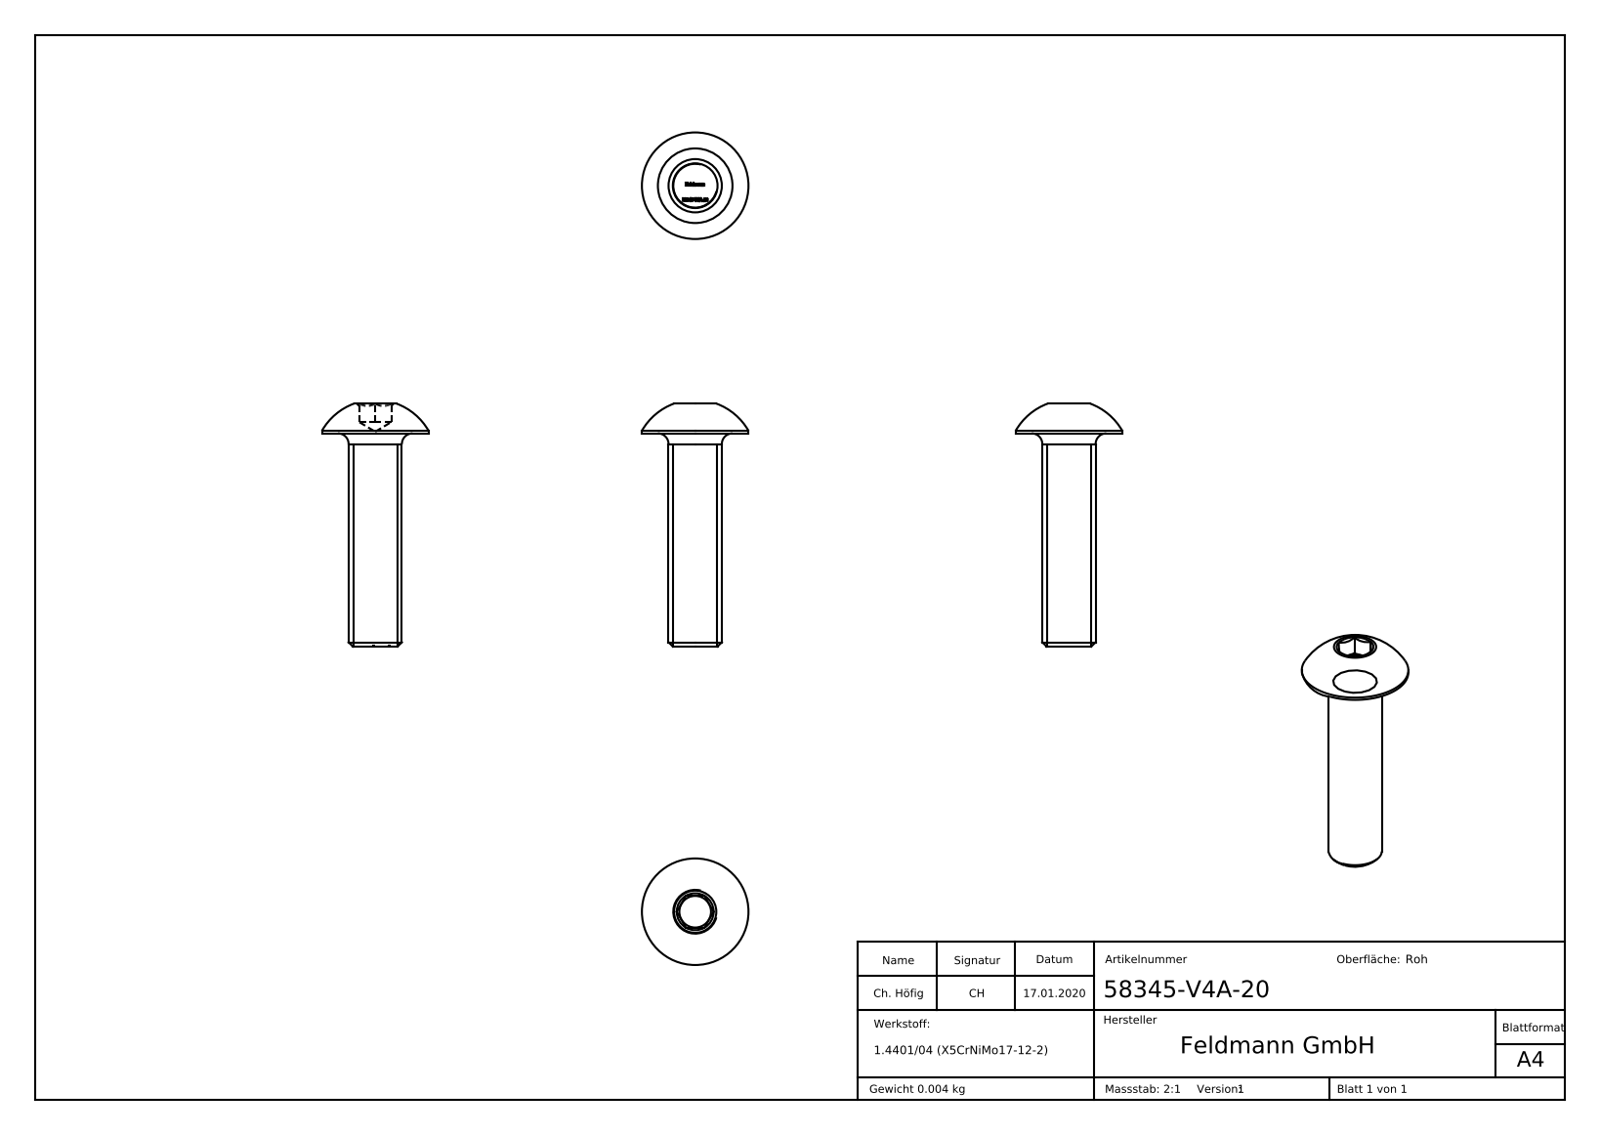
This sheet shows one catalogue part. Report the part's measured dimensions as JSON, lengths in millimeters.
{"part_name": "58345-V4A-20", "step_written_by": "SolidWorks 2015 (CONFIG_CONTROL_DESIGN)", "units": "millimeters", "bodies": {"solids": 1, "faces": 288, "planar": 166, "cylindrical": 2, "other": 120}, "overall_size": [24.8, 10, 10], "volume_mm3": 523, "surface_area_mm2": 516, "round_bosses_or_shafts": [[10, 1], [5, 1]], "face_to_face_distances": [20, 3, 2.8, 22.8, 1.75, 1.05, 21.05, 22.7, 20.95, 19.9]}
